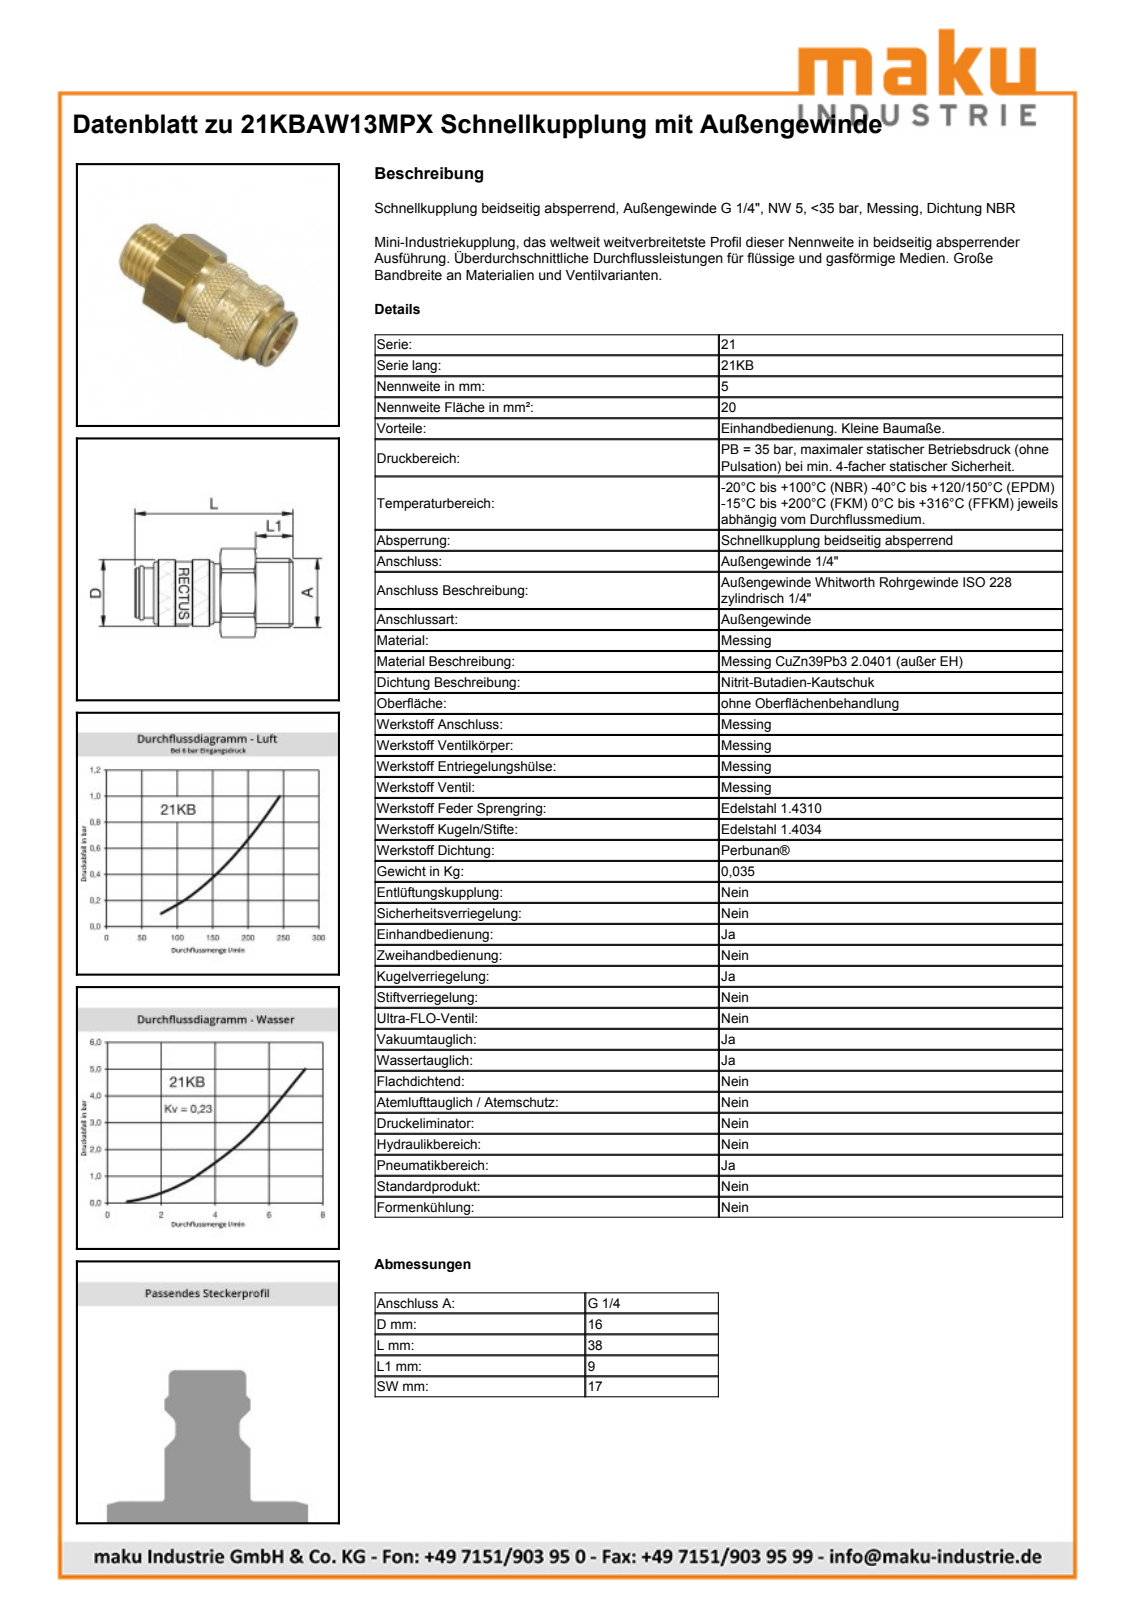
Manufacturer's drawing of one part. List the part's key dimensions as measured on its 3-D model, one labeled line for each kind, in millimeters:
Part name (STEP PRODUCT): D107125
STEP written by: Autodesk Inventor 2013 (AUTOMOTIVE_DESIGN)
Units: millimetres
Bodies: 2 solids, 452 faces (149 planar, 60 cylindrical, 243 other)
Overall size (bounding box): 38.15 × 19.02 × 18.21
Volume: 6 547 mm³ · Surface area: 3 690 mm²
Round holes (diameter × count): ⌀11.46 ×1, ⌀12.15 ×1, ⌀14 ×1
Round bosses / shafts (diameter × count): ⌀16.15 ×1, ⌀15.1 ×1, ⌀13.16 ×1, ⌀12 ×1, ⌀11.4 ×1, ⌀11.15 ×1
Partial cylindrical surfaces — rounded edges, fillets, slot ends (radius × count): R5.49 ×1, R7.45 ×1, R9.57 ×1
Main face-to-face distances: 17, 38.15, 29.15, 9, 4.45, 20.6, 8.55, 17.55, 16.15, 13
